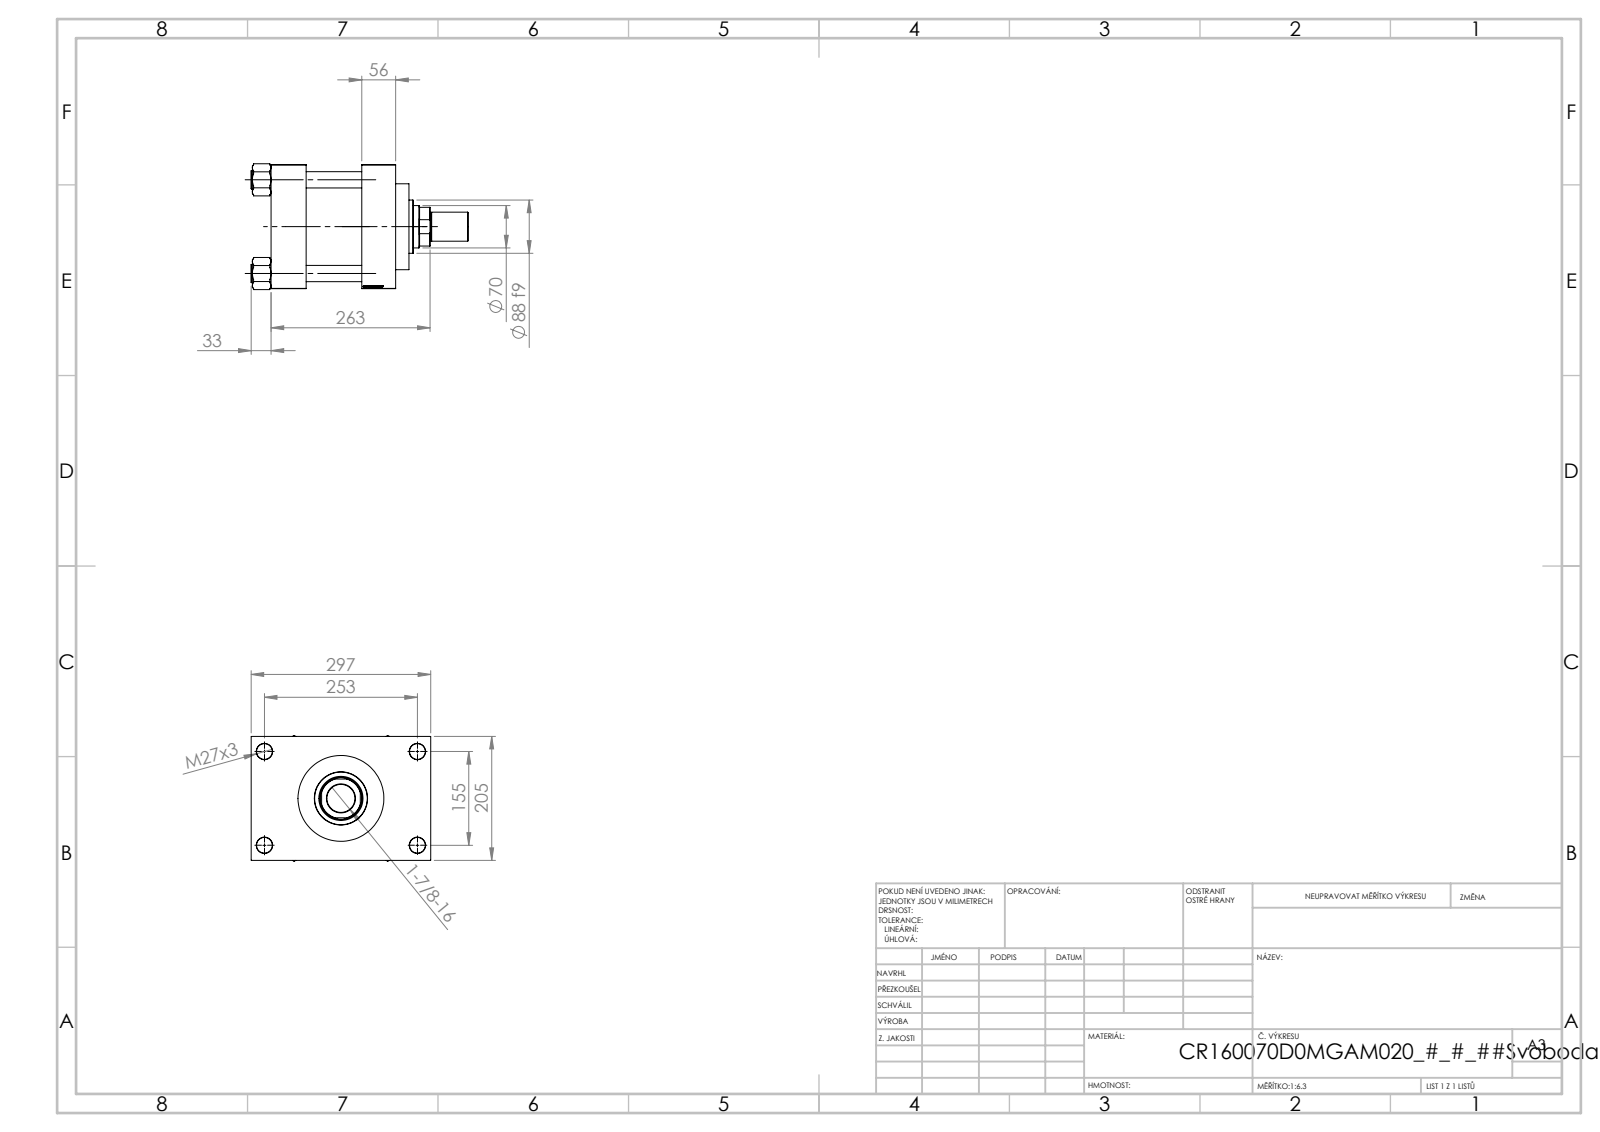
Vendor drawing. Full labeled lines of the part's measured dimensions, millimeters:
Part name (STEP PRODUCT): NUT_M5_D; V215CR_VCP_D; V215_VC_A; ROD_END_AH (+2 more)
STEP written by: SolidWorks 2019 (CONFIG_CONTROL_DESIGN)
Units: millimetres
Bodies: 12 solids, 1163 faces (548 planar, 91 cylindrical, 524 other)
Overall size (bounding box): 359 × 297 × 208.14
Volume: 8 009 000 mm³ · Surface area: 738 229 mm²
Round holes (diameter × count): ⌀26 ×4, ⌀27 ×4, ⌀7 ×2, ⌀33.24 ×2, ⌀45 ×2, ⌀46.5 ×1, ⌀70 ×1, ⌀73 ×1, ⌀120 ×1, ⌀142 ×1, ⌀160 ×1
Round bosses / shafts (diameter × count): ⌀30 ×4, ⌀166 ×1, ⌀88 ×1, ⌀48 ×1, ⌀46 ×1
Partial cylindrical surfaces — rounded edges, fillets, slot ends (radius × count): R34 ×1
Main face-to-face distances: 58, 150, 92, 206, 148, 56, 205, 46, 251, 72
Hole centre spacings: 49.05, 109.53, 148.35, 154.9, 162.53, 203.95, 256.13, 155
